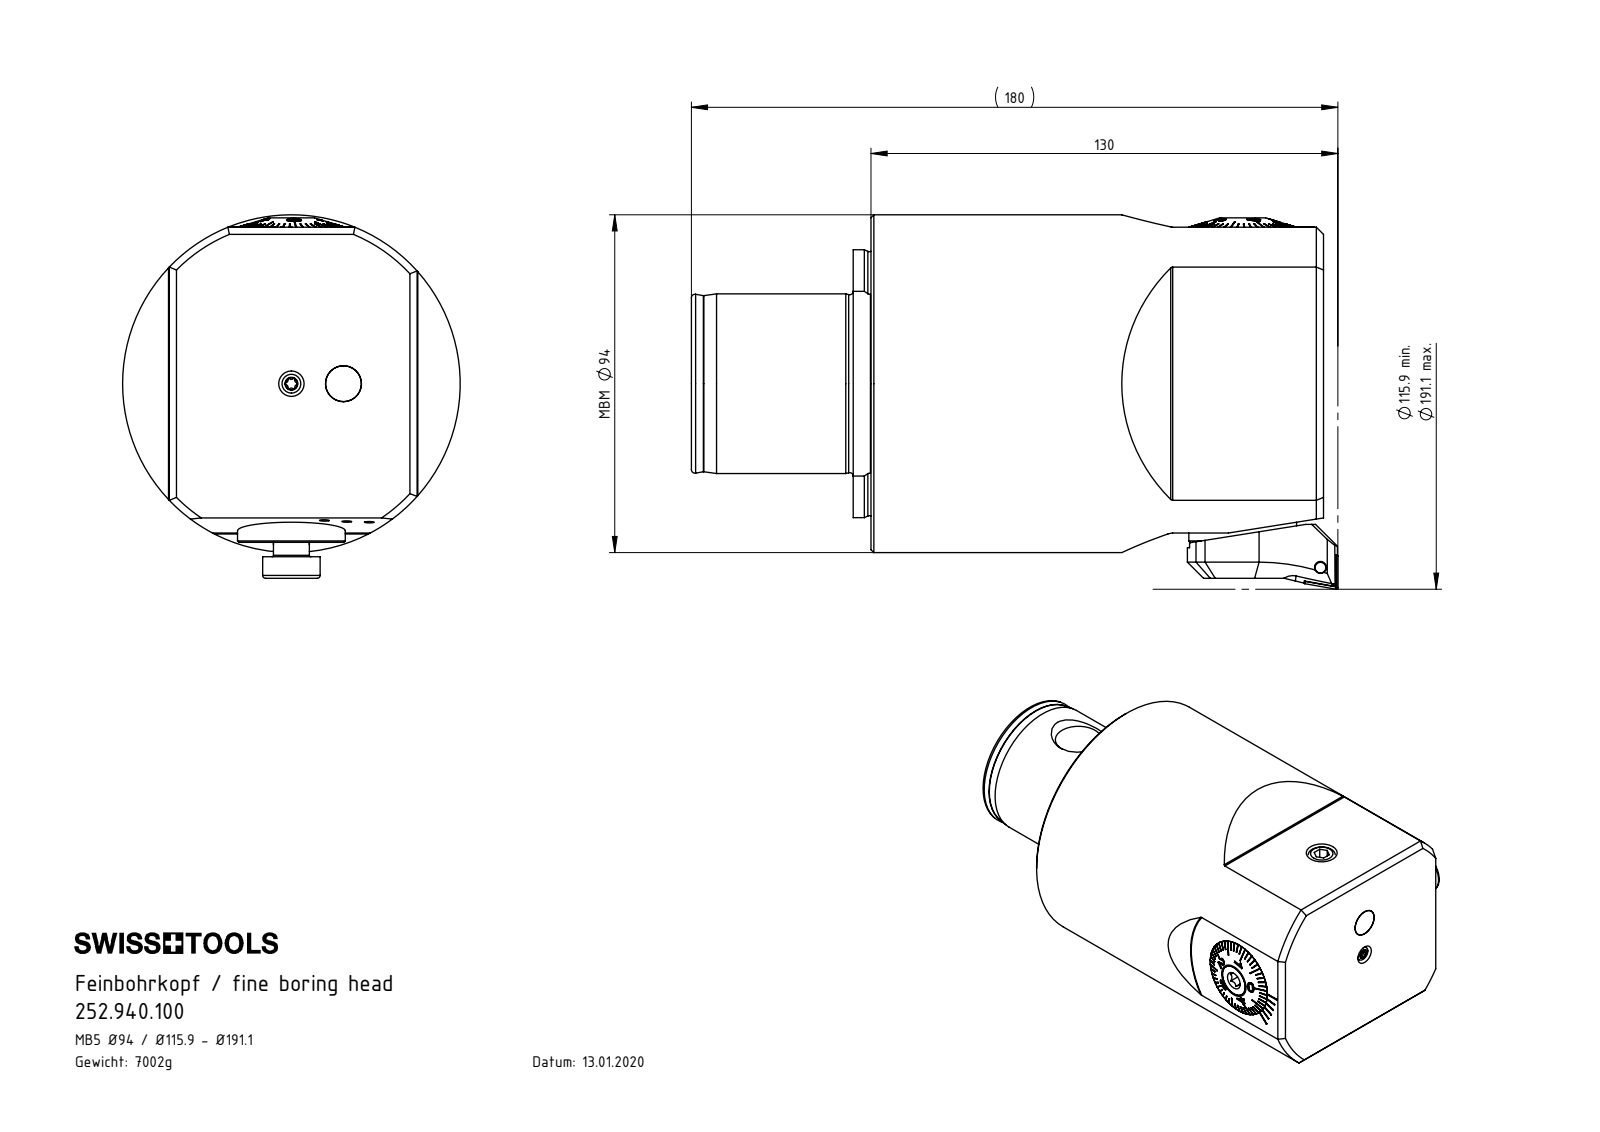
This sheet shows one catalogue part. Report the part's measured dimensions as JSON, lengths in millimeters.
{"part_name": "MB9.F94.K21.130; Klebstoff D10; A55-BG3.011.033_A_gekürzt; F94-BG1.014.082 (+8 more)", "step_written_by": "SolidWorks 2011 (CONFIG_CONTROL_DESIGN)", "units": "millimeters", "bodies": {"solids": 13, "faces": 698, "planar": 287, "cylindrical": 127, "other": 284}, "overall_size": [176, 94, 94], "volume_mm3": 951420, "surface_area_mm2": 93393, "round_holes": [[3.3, 8], [8.5, 3], [4.2, 1], [8, 1], [10, 1], [11.75, 1], [12, 1], [12.4, 1], [12.5, 1], [13, 1], [14, 1], [14.2, 1]], "round_bosses_or_shafts": [[4, 2], [94, 1], [50, 1], [30, 1], [29.98, 1], [29.9, 1], [25, 1], [18, 1]], "partial_cylinders_radius": [[0.34, 6], [0.59, 6], [3.2, 5], [0.5, 2], [1, 1], [37.27, 1]], "face_to_face_distances": [126, 50, 176, 4.95, 45.05, 130.95, 49.85, 4.8, 126.15, 7.93], "hole_center_spacings": [14.5, 22.54, 30.62, 32.5, 33.88, 35, 55.09, 127.7]}
